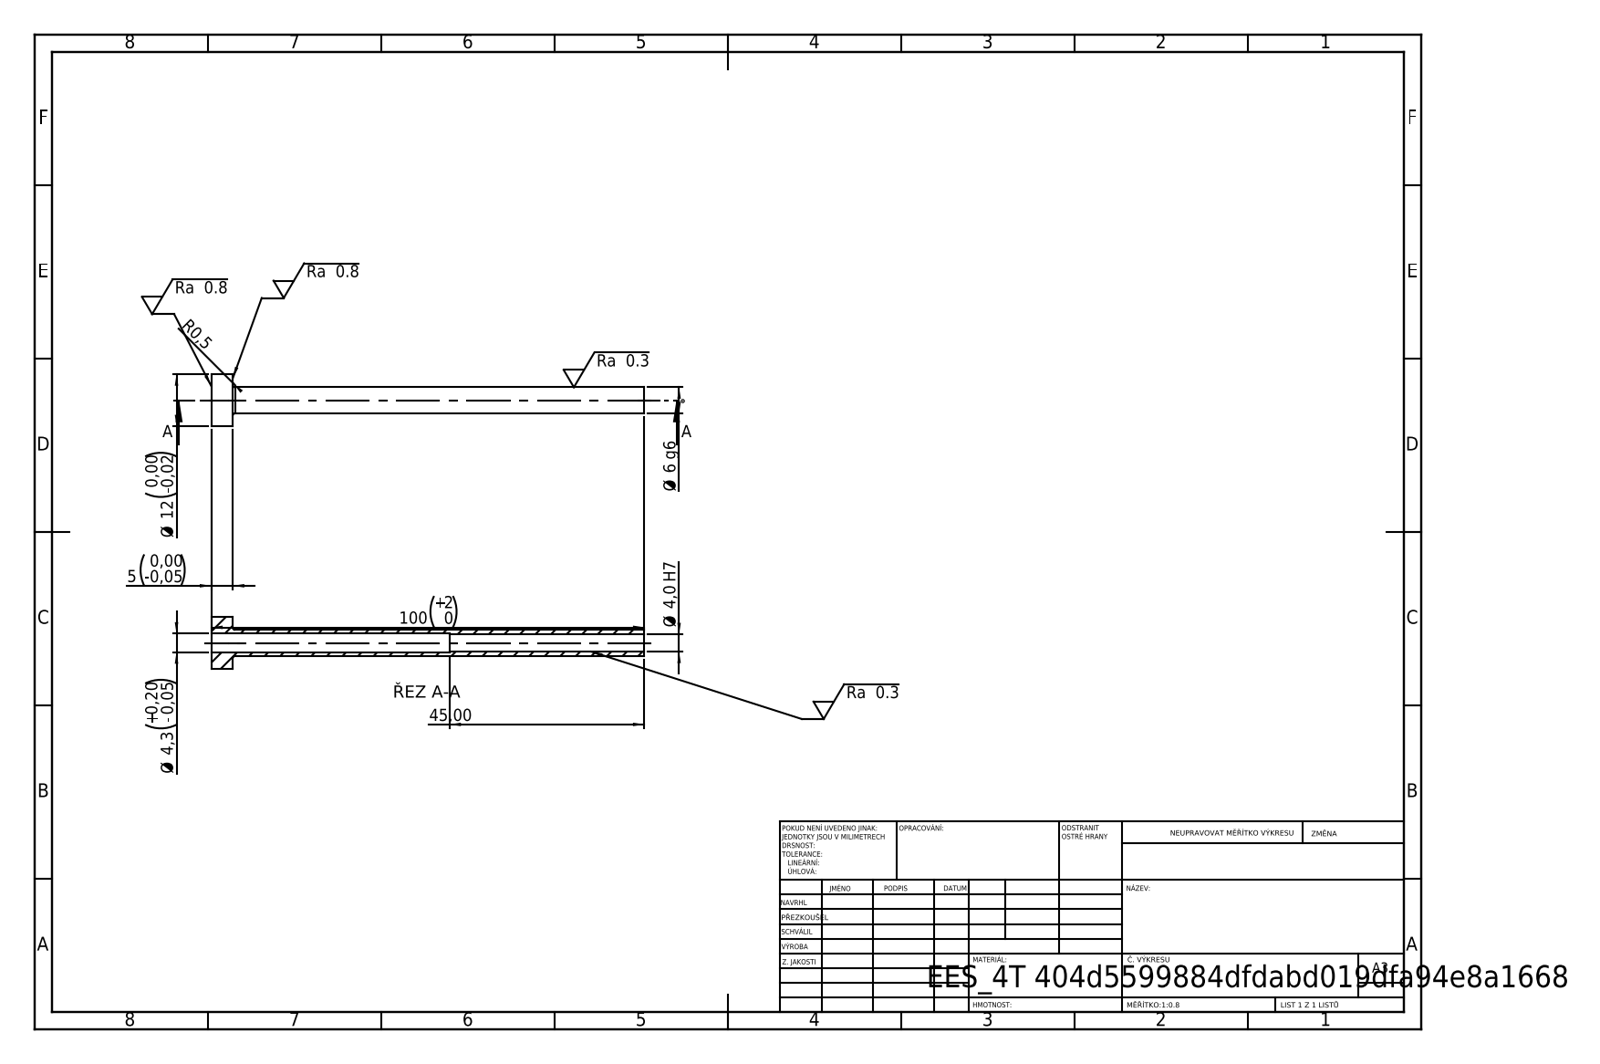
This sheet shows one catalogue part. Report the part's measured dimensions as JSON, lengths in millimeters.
{"step_written_by": "SolidWorks 2019 (CONFIG_CONTROL_DESIGN)", "units": "millimeters", "bodies": {"solids": 1, "faces": 14, "planar": 4, "cylindrical": 8, "other": 2}, "overall_size": [100, 12, 12], "volume_mm3": 1888, "surface_area_mm2": 3485, "round_holes": [[4, 1], [4.3, 1]], "round_bosses_or_shafts": [[12, 1], [6, 1]], "face_to_face_distances": [5, 100, 95, 55, 50, 45]}
